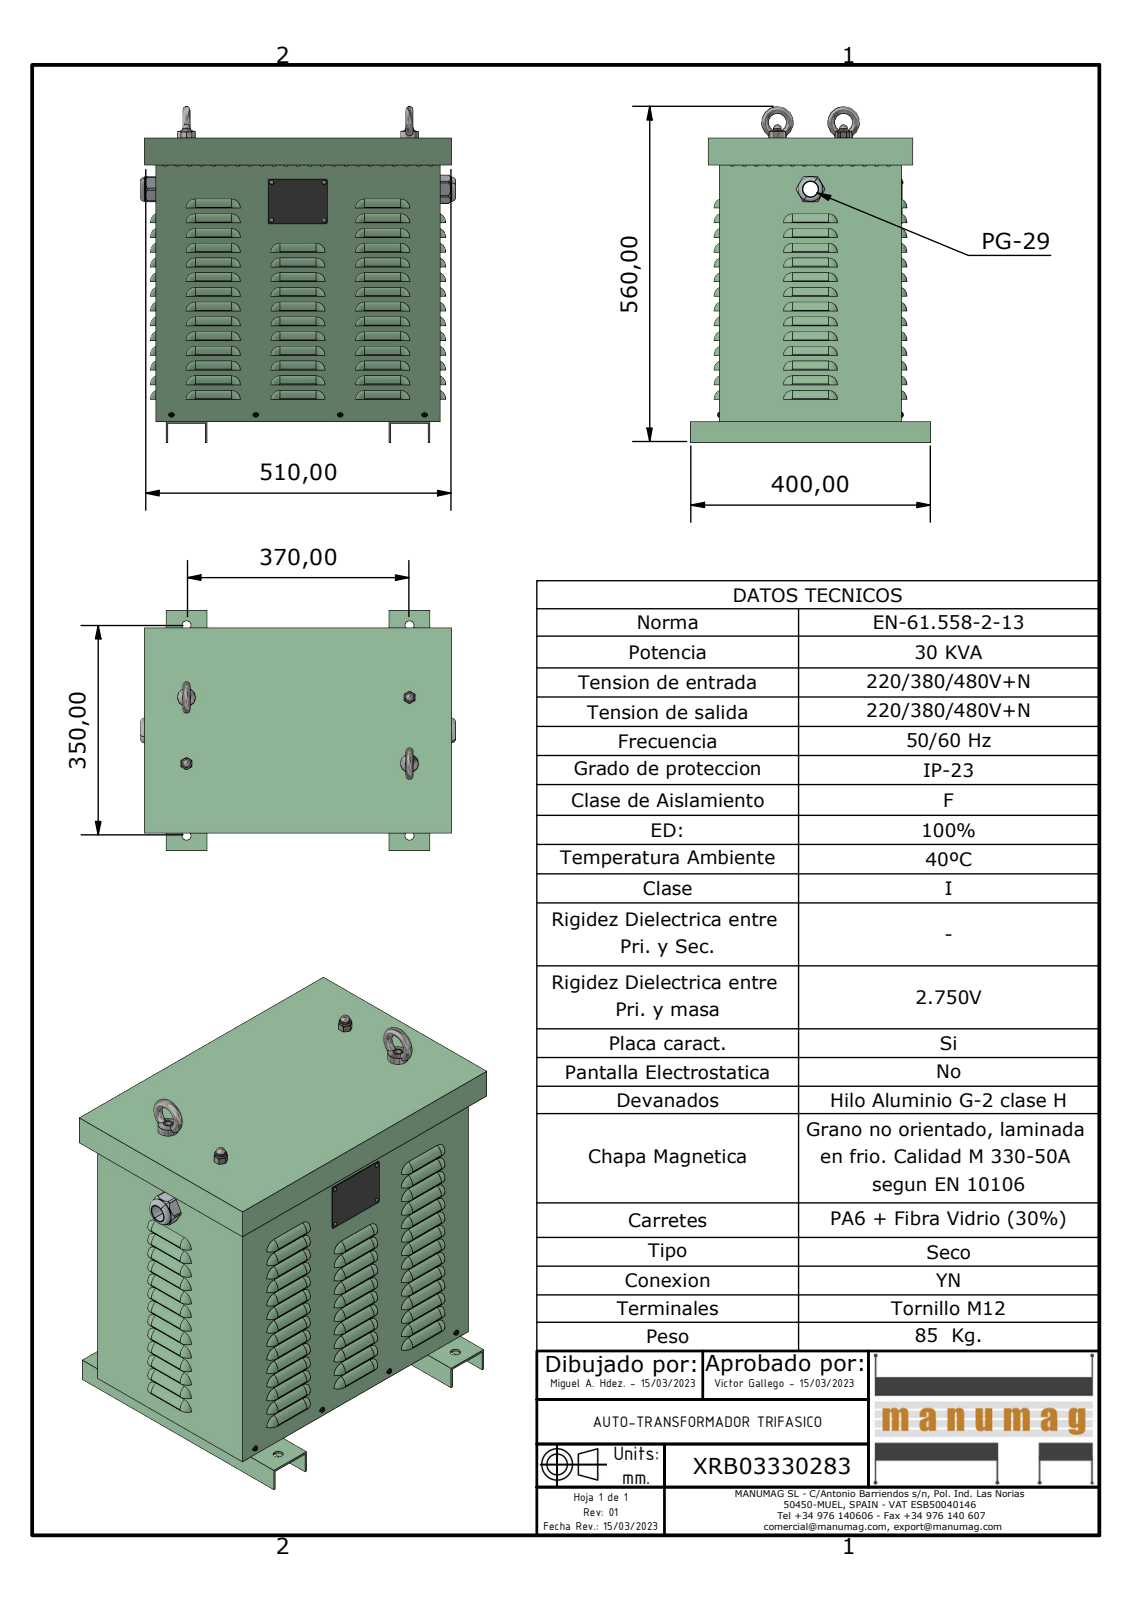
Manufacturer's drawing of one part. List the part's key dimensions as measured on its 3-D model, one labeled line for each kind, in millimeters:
Part name (STEP PRODUCT): XRB03330283; JE030 CUERPO; JE030 BASE; JE030 PATAS (+7 more)
STEP written by: Autodesk Inventor 2023 (AUTOMOTIVE_DESIGN)
Units: millimetres
Bodies: 24 solids, 2363 faces (789 planar, 948 cylindrical, 626 other)
Overall size (bounding box): 560 × 523.4 × 400
Volume: 2 982 000 mm³ · Surface area: 2 640 000 mm²
Round holes (diameter × count): ⌀11 ×260, ⌀15 ×8, ⌀4 ×4, ⌀5 ×4, ⌀10.11 ×4, ⌀14 ×4, ⌀25 ×1, ⌀38 ×1
Round bosses / shafts (diameter × count): ⌀4 ×4, ⌀3.62 ×4, ⌀3.2 ×4, ⌀30 ×2, ⌀18 ×2, ⌀13.6 ×2, ⌀40.8 ×1, ⌀37.3 ×1
Partial cylindrical surfaces — rounded edges, fillets, slot ends (radius × count): R14 ×104, R5 ×74, R7 ×54, R15 ×54, R3.22 ×12, R2.5 ×8, R2 ×4, R23.85 ×1
Main face-to-face distances: 2, 470, 301, 472, 468, 299, 303, 19, 3, 21
Hole centre spacings: 31.76, 71.59, 15, 28, 70, 44.6, 99.14, 140.8
